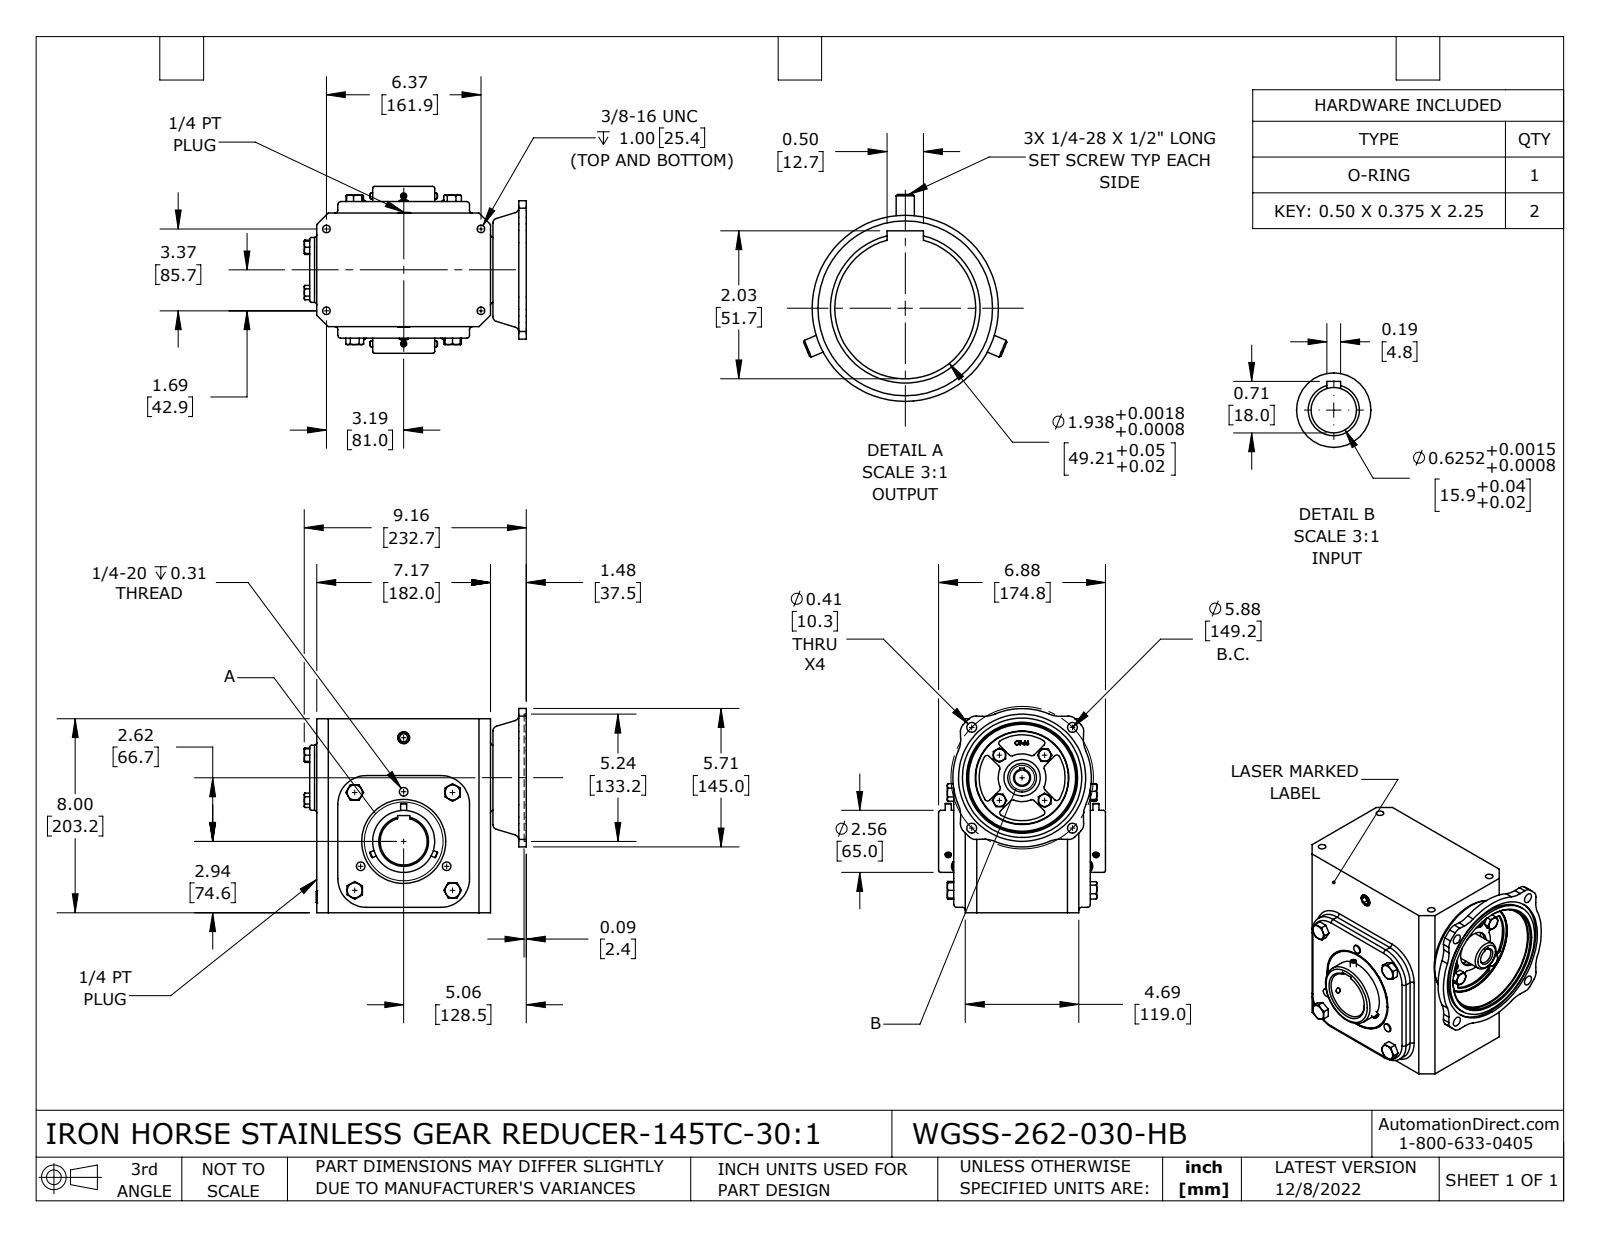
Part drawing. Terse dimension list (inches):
name: WGSS-262-030-HB
written by: SolidWorks 2021 (CONFIG_CONTROL_DESIGN)
unit: in
bodies: 7 solids, 669 faces (285 planar, 191 cylindrical, 193 other)
size: 9.16 × 8.417 × 6.882
volume: 289.1 in³; area: 423.6 in²
holes: 6× ⌀0.213, 4× ⌀0.313, 4× ⌀0.406, 1× ⌀0.625, 1× ⌀0.866, 1× ⌀1.496, 1× ⌀1.772, 1× ⌀1.937, 1× ⌀2.047, 1× ⌀3.819, 1× ⌀4.5, 1× ⌀5.244
bosses: 6× ⌀0.25, 3× ⌀0.354, 1× ⌀4.921, 1× ⌀3.465, 1× ⌀2.559, 1× ⌀1.181
rounds: 40× R0.118, 12× R0.394, 12× R1.181, 4× R0.079, 1× R0.984, 1× R1.772, 1× R2.854, 1× R3.27
face distances: 0.472, 5.157, 8, 7.165, 4.685, 5.63, 7.461, 7.71, 0.295, 1.161
hole spacings: 2.937, 3.465, 4.154, 5.707, 6.094, 3.375, 5.875, 6.375
